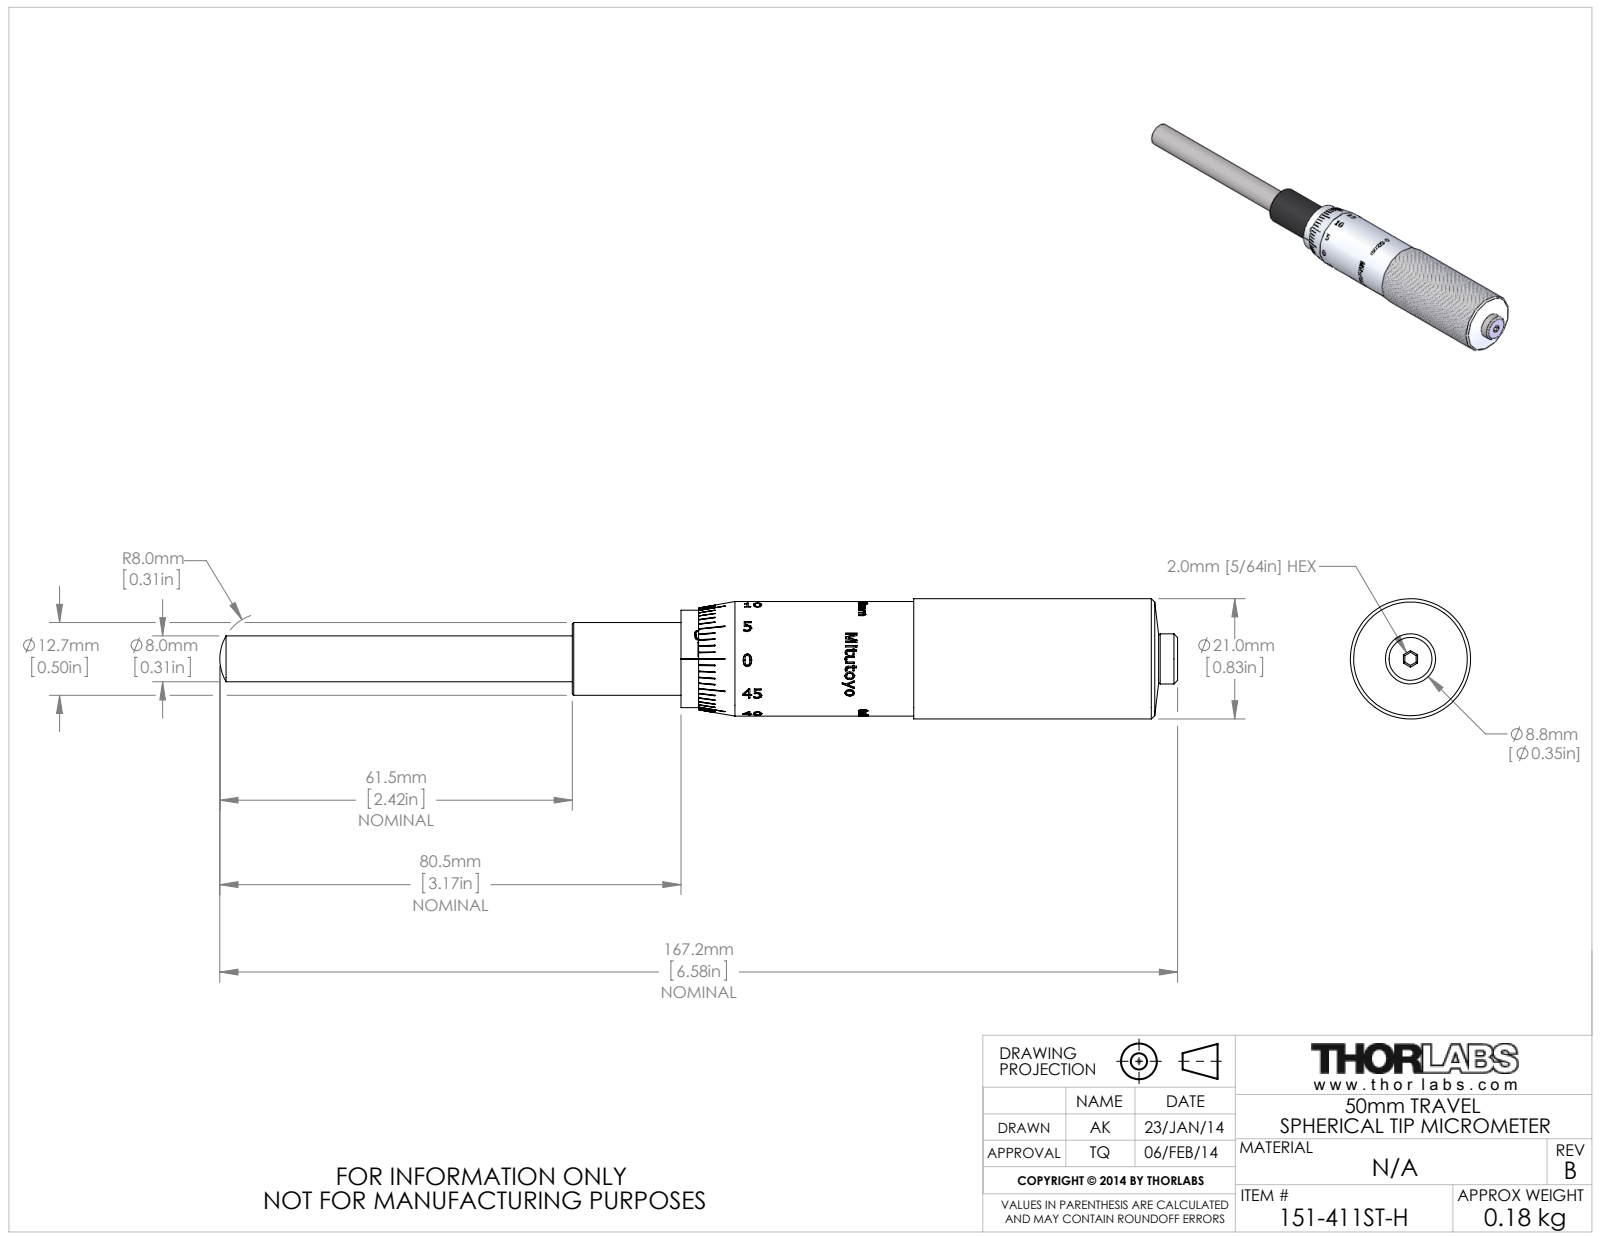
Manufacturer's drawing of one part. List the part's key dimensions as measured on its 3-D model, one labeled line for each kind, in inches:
Part name (STEP PRODUCT): TTN017745-E0W
STEP written by: SolidWorks 2012 (AUTOMOTIVE_DESIGN)
Units: inches
Bodies: 3 solids, 1820 faces (985 planar, 233 cylindrical, 602 other)
Overall size (bounding box): 6.584 × 0.827 × 0.827
Volume: 1.931 in³ · Surface area: 31.28 in²
Round holes (diameter × count): ⌀0.157 ×1, ⌀0.315 ×1
Round bosses / shafts (diameter × count): ⌀0.827 ×1, ⌀0.787 ×1, ⌀0.669 ×1, ⌀0.543 ×1, ⌀0.5 ×1, ⌀0.345 ×1, ⌀0.137 ×1
Partial cylindrical surfaces — rounded edges, fillets, slot ends (radius × count): R0.334 ×1, R0.351 ×1, R0.381 ×1, R0.393 ×1
Main face-to-face distances: 2.698, 2.697, 3.283, 0.587, 0.585, 0.748, 3.445, 3.446, 4.031, 2.953
